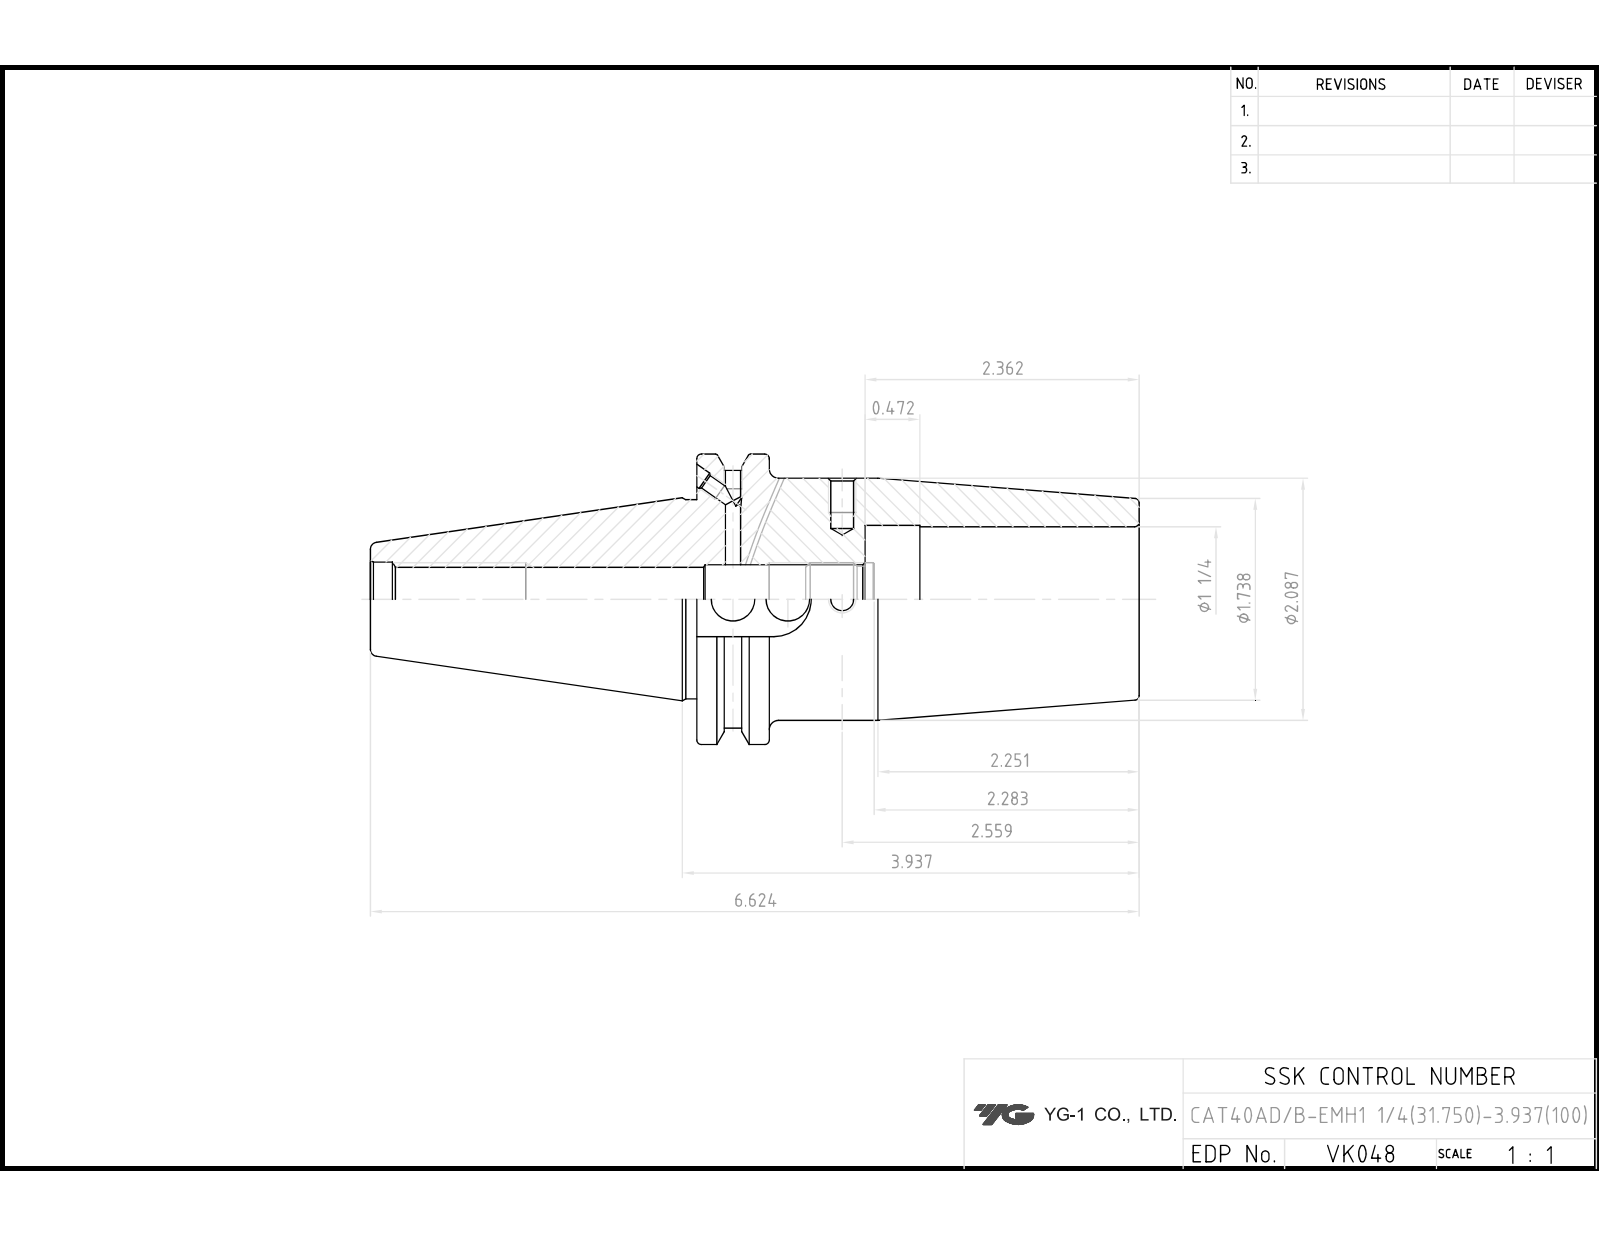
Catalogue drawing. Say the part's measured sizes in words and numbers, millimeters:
The part is named "LO-CAT40ADB-SFH31.75-100". Its 3-D file was written by "Autodesk Inventor 2022 (AUTOMOTIVE_DESIGN)". It is 1 solid with 87 faces: 34 planar, 31 cylindrical and 22 other. Overall it measures 168.25 by 63.5 by 61.09 millimeters. Its volume is 206 109 cubic millimeters and its surface area 39 879 square millimeters. Round holes: 4 of diameter 3.24, 2 of diameter 4, 2 of diameter 4.2, 1 of diameter 9.53, 1 of diameter 13, 1 of diameter 13.39, 1 of diameter 14.92, 1 of diameter 16.3, 1 of diameter 31.75, 1 of diameter 32.95. Round bosses or shafts: 1 of diameter 63.5, 1 of diameter 53, 1 of diameter 43.6. Partial cylindrical surfaces (rounded edges, fillets, slot ends): 1 of radius 8.19, 1 of radius 28.15. The main face-to-face distances are 36.83, 96.83, 60, 15.88, 20.95, 80.95, 47.6, 16.38, 71.42, 87.3.
